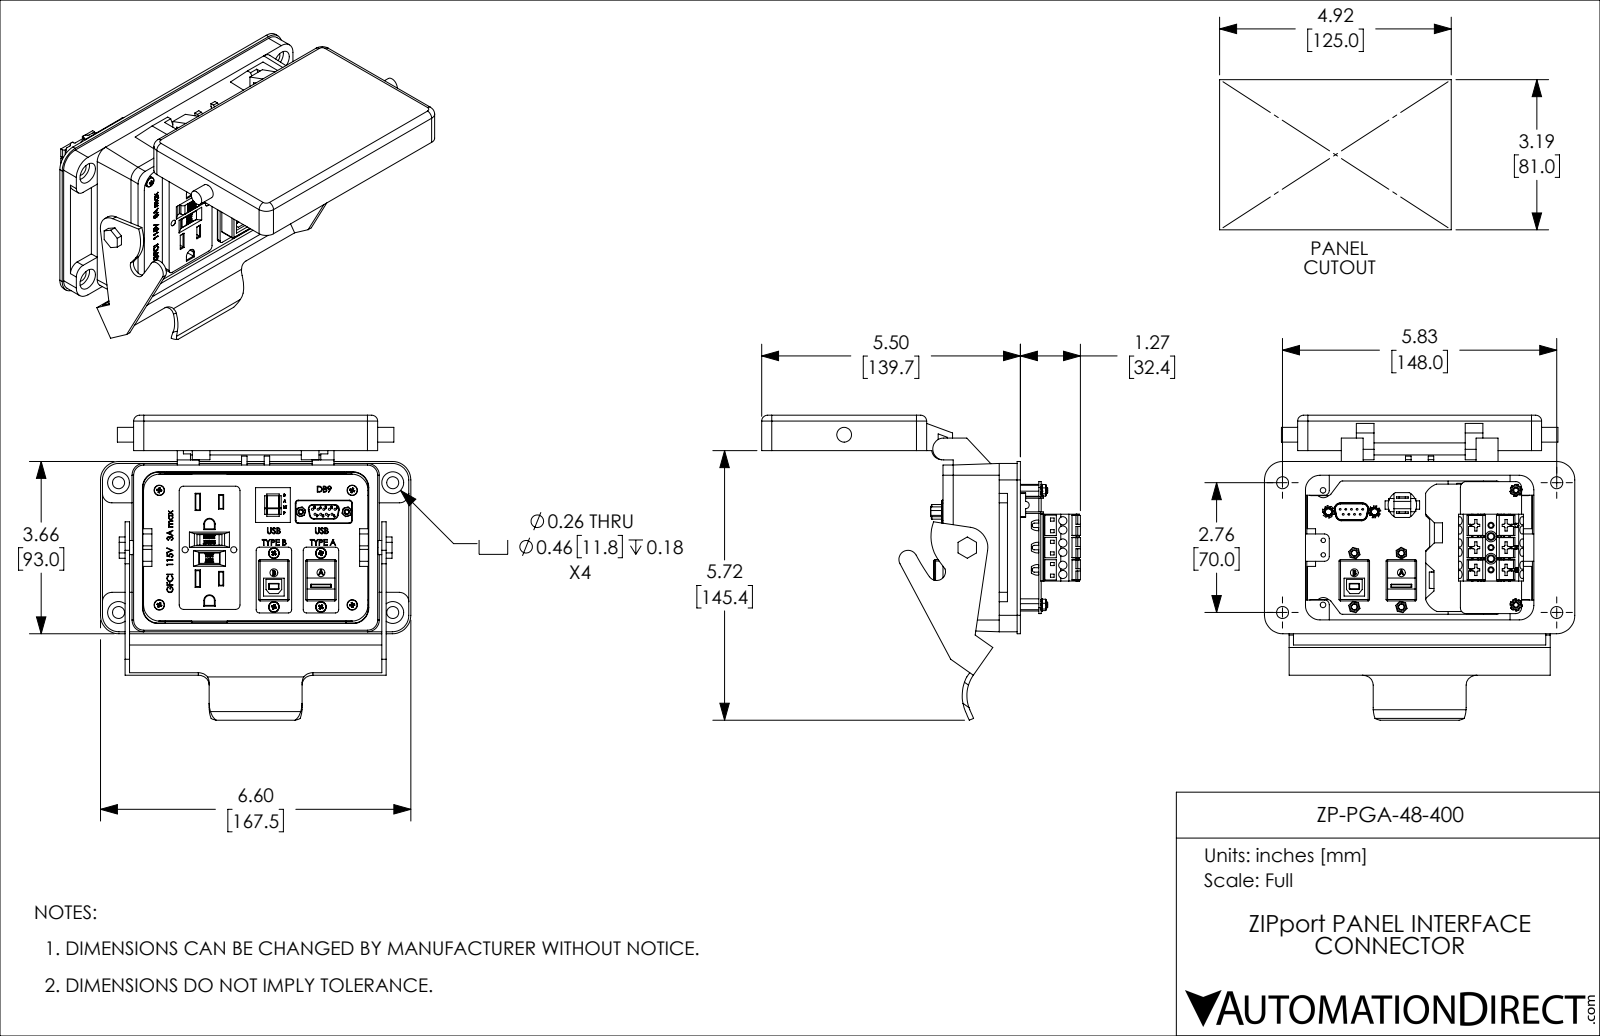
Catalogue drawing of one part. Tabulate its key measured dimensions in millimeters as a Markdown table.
| quantity | value |
| --- | --- |
| part name | ZP-PGA-48-400 |
| STEP written by | SolidWorks 2016 (CONFIG_CONTROL_DESIGN) |
| units | millimeters |
| bodies | 1 solid, 3330 faces (2019 planar, 647 cylindrical, 664 other) |
| overall size | 172.05 × 167.51 × 164.5 |
| volume | 385 918 mm³ |
| surface area | 172 213 mm² |
| round holes (diameter × count) | 3.66 × 8, 4.4 × 6, 1.14 × 5, 1.14 × 4, 2.41 × 4, 3.3 × 4, 3.6 × 4, 6.5 × 4, 11.79 × 4, 2.3 × 3, 2.29 × 2, 2.46 × 2 |
| round bosses / shafts (diameter × count) | 0.97 × 9, 5.6 × 8, 3 × 8, 5.75 × 4, 4.45 × 4, 5.2 × 3, 8 × 2, 2.76 × 2 |
| partial cylindrical surfaces (radius × count) | 0.25 × 32, 0.76 × 30, 2 × 12, 0.32 × 10, 2.54 × 10, 0.13 × 8, 1.78 × 8, 3.17 × 8 |
| main face-to-face distances | 3.81, 1.22, 34.48, 35.7, 2.37, 138.53, 85.25, 45.66, 85.35, 2.38 |
| hole center spacings | 3.05, 12, 6, 38.09, 44.69, 129.78, 131.87, 3.17 |
